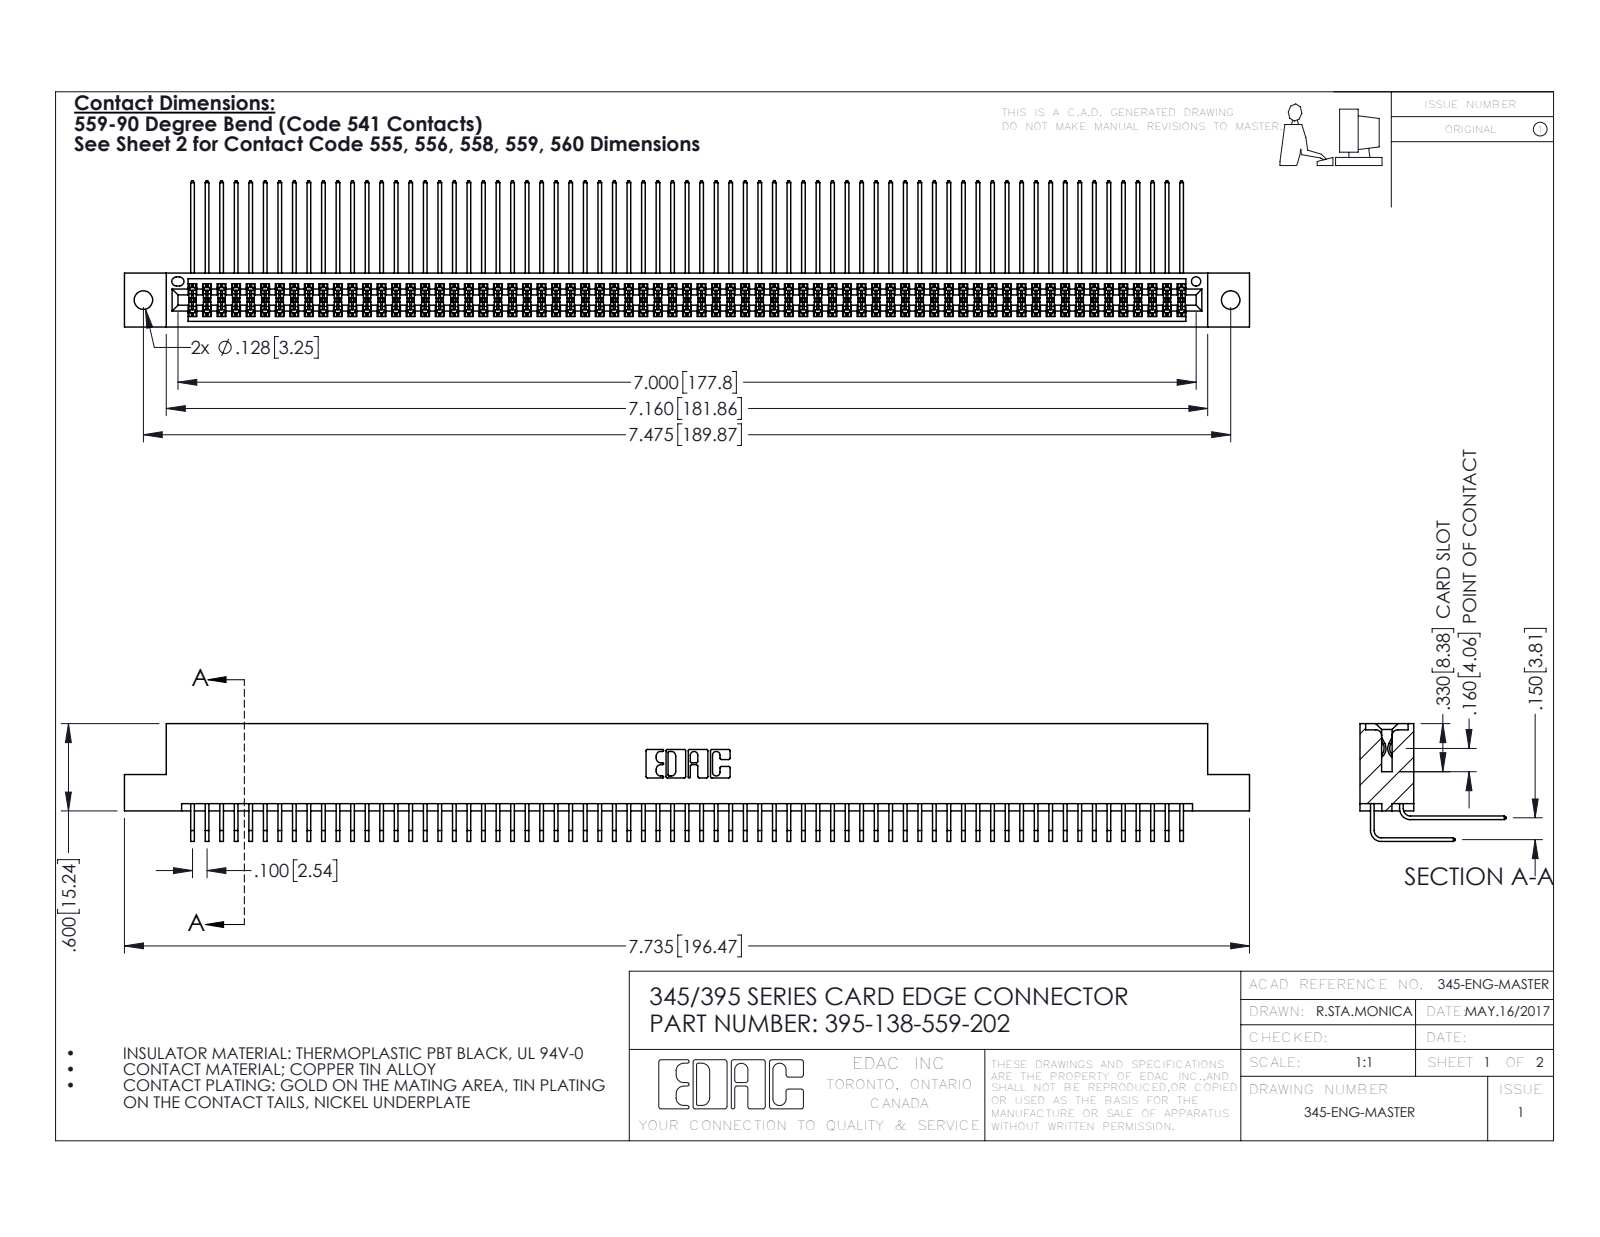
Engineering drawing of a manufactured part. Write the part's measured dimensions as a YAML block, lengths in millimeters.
part_name: "395-138-559-202; 345-292-001_559 Tail - 2; 345 Part_Flush Mounting Lugs - 0.128 Dia; 345-292-001_558 559 Tail - 1"
step_written_by: "SolidWorks 2016 (CONFIG_CONTROL_DESIGN)"
units: millimeters
bodies: {solids: 139, faces: 7302, planar: 4910, cylindrical: 2392, other: 0}
overall_size: [196.5, 25.5, 20.5]
volume: 20090
surface_area: 33700
round_holes:
  - {diameter: 3.3, count: 2}
  - {diameter: 1.6, count: 1}
partial_cylinders:
  - {radius: 0.2, count: 275}
  - {radius: 0.3, count: 22}
  - {radius: 0.2, count: 6}
  - {radius: 0.8, count: 6}
  - {radius: 0.7, count: 3}
  - {radius: 0.4, count: 2}
  - {radius: 0.5, count: 2}
  - {radius: 0.6, count: 2}
face_to_face_distances: [1.8, 7.6, 5.1, 9.4, 2.5, 6.9, 0.6, 5.7, 4.4, 3.8]
hole_center_spacings: [6.9, 183.9, 189.9]
